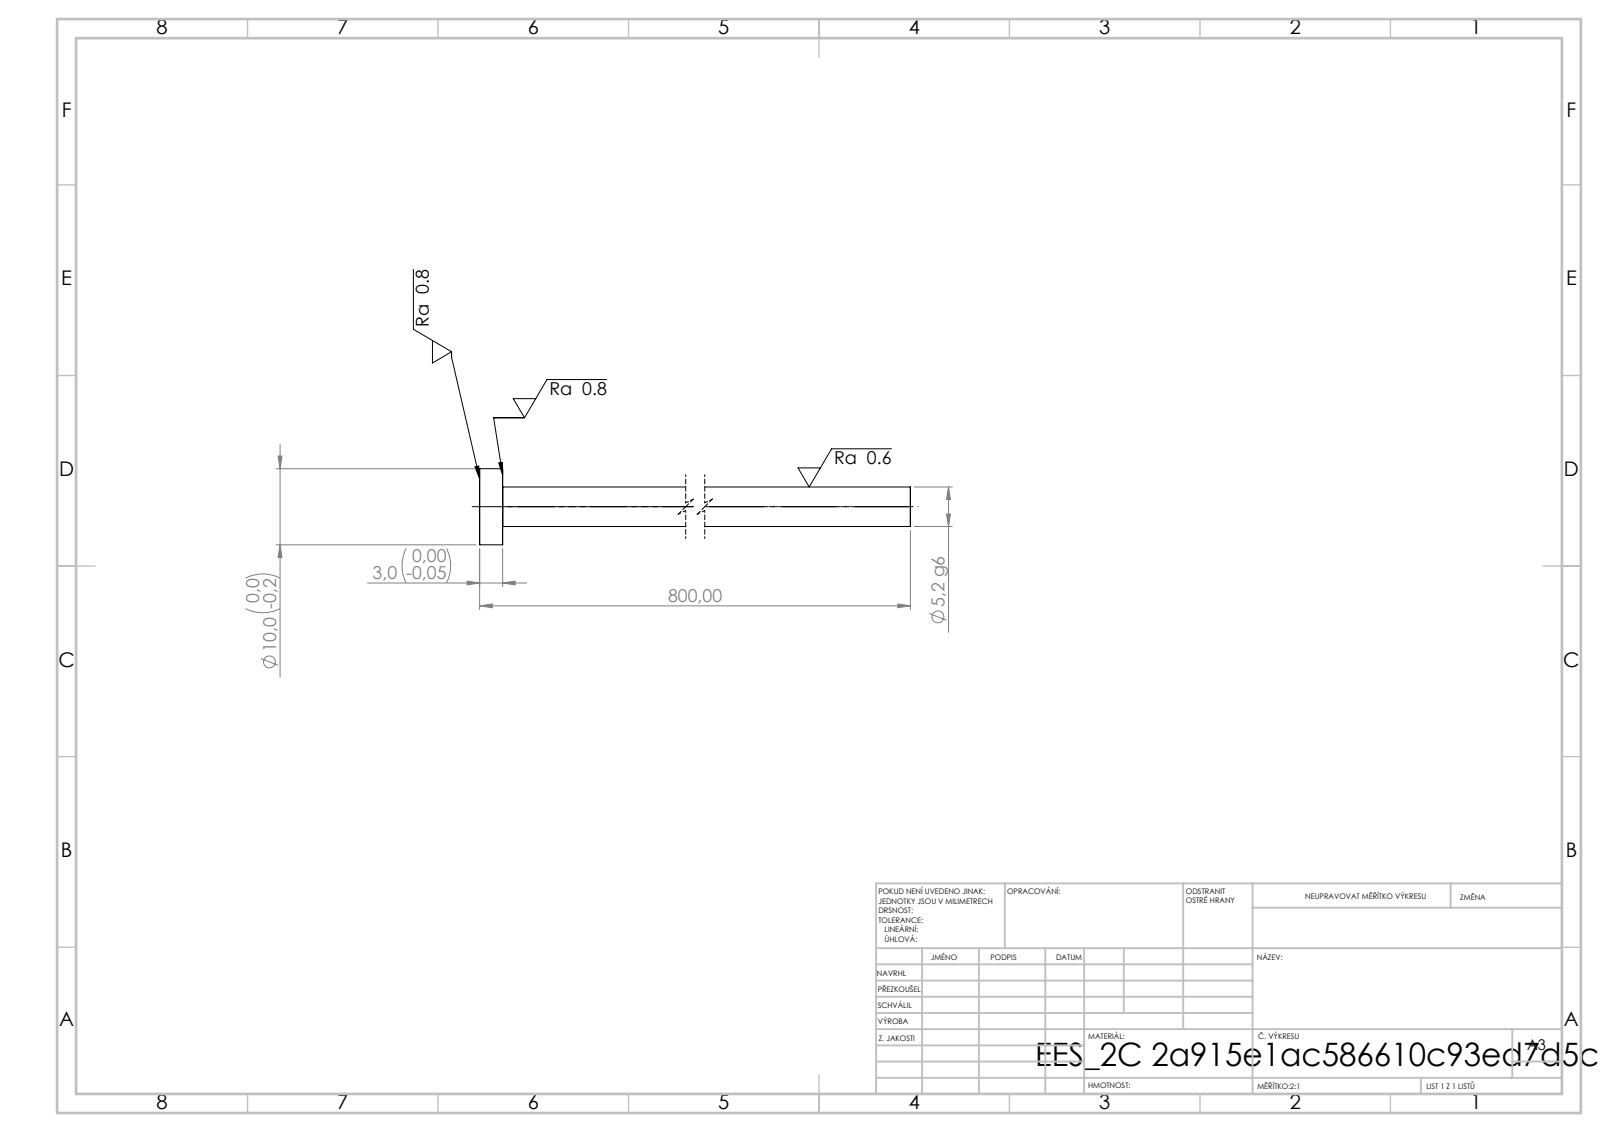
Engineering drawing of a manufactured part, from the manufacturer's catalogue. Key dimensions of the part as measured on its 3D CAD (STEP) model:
STEP written by: SolidWorks 2019 (CONFIG_CONTROL_DESIGN)
Units: millimetres
Bodies: 1 solid, 7 faces (3 planar, 4 cylindrical, 0 other)
Overall size (bounding box): 800 × 10 × 10
Volume: 17 162 mm³ · Surface area: 13 271 mm²
Round bosses / shafts (diameter × count): ⌀10 ×1, ⌀5.2 ×1
Main face-to-face distances: 3, 800, 797
